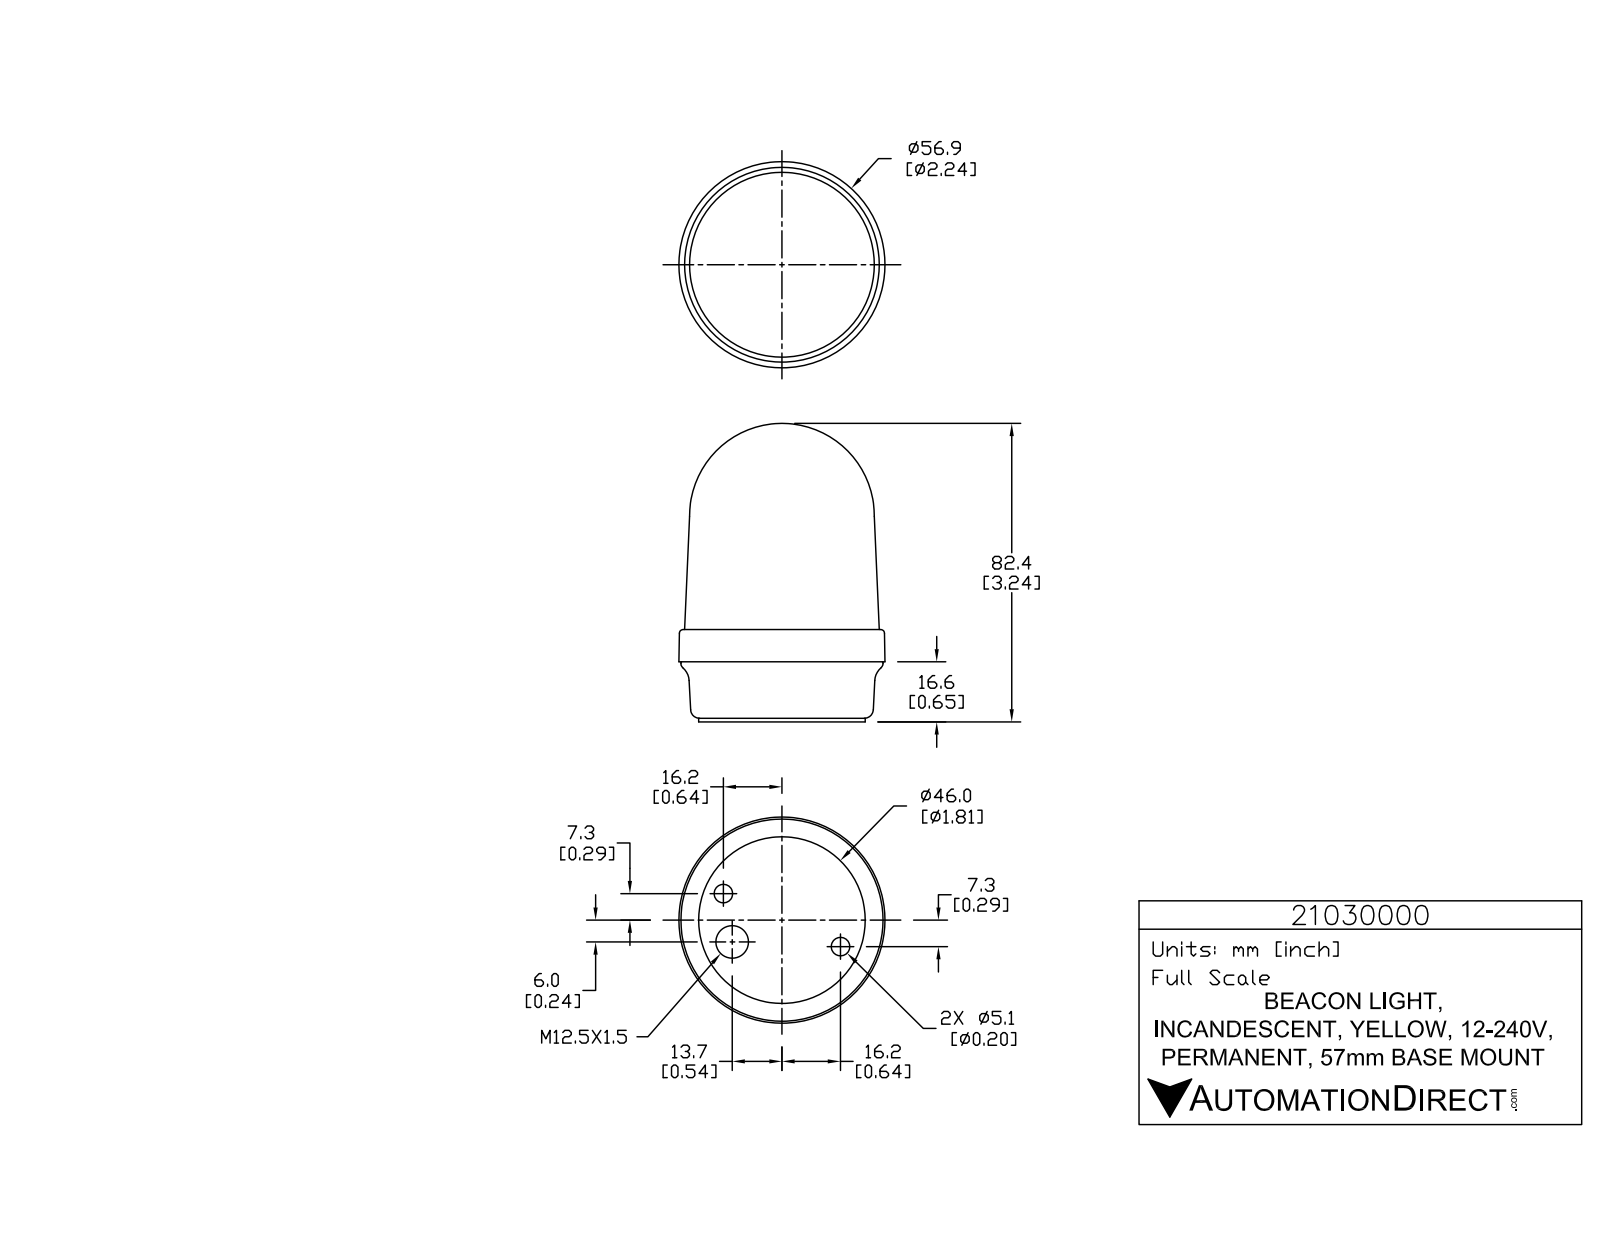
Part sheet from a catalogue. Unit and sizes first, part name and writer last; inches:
Units: inches
Overall size (bounding box): 3.244 × 2.24 × 2.24
Round holes (diameter × count): ⌀0.039 ×3, ⌀0.201 ×2, ⌀0.354 ×1
Round bosses / shafts (diameter × count): ⌀0.226 ×3, ⌀0.056 ×3, ⌀2.197 ×1, ⌀1.811 ×1
Partial cylindrical surfaces — rounded edges, fillets, slot ends (radius × count): R0.008 ×6, R0.008 ×6, R0.008 ×6, R0.131 ×6, R0.004 ×3, R0.005 ×3, R0.008 ×3, R0.008 ×3
Main face-to-face distances: 0.039, 0.654, 0.614, 1.004, 0.965, 0.35, 0.418, 1.422, 1.382, 0.768
Hole centre spacings: 0.534, 1.179, 1.398
Volume: 9.7 in³ · Surface area: 24.8 in²
Bodies: 1 solid, 778 faces (526 planar, 160 cylindrical, 92 other)
Part name (STEP PRODUCT): 21030000
STEP written by: SolidWorks 2015 (AUTOMOTIVE_DESIGN)
